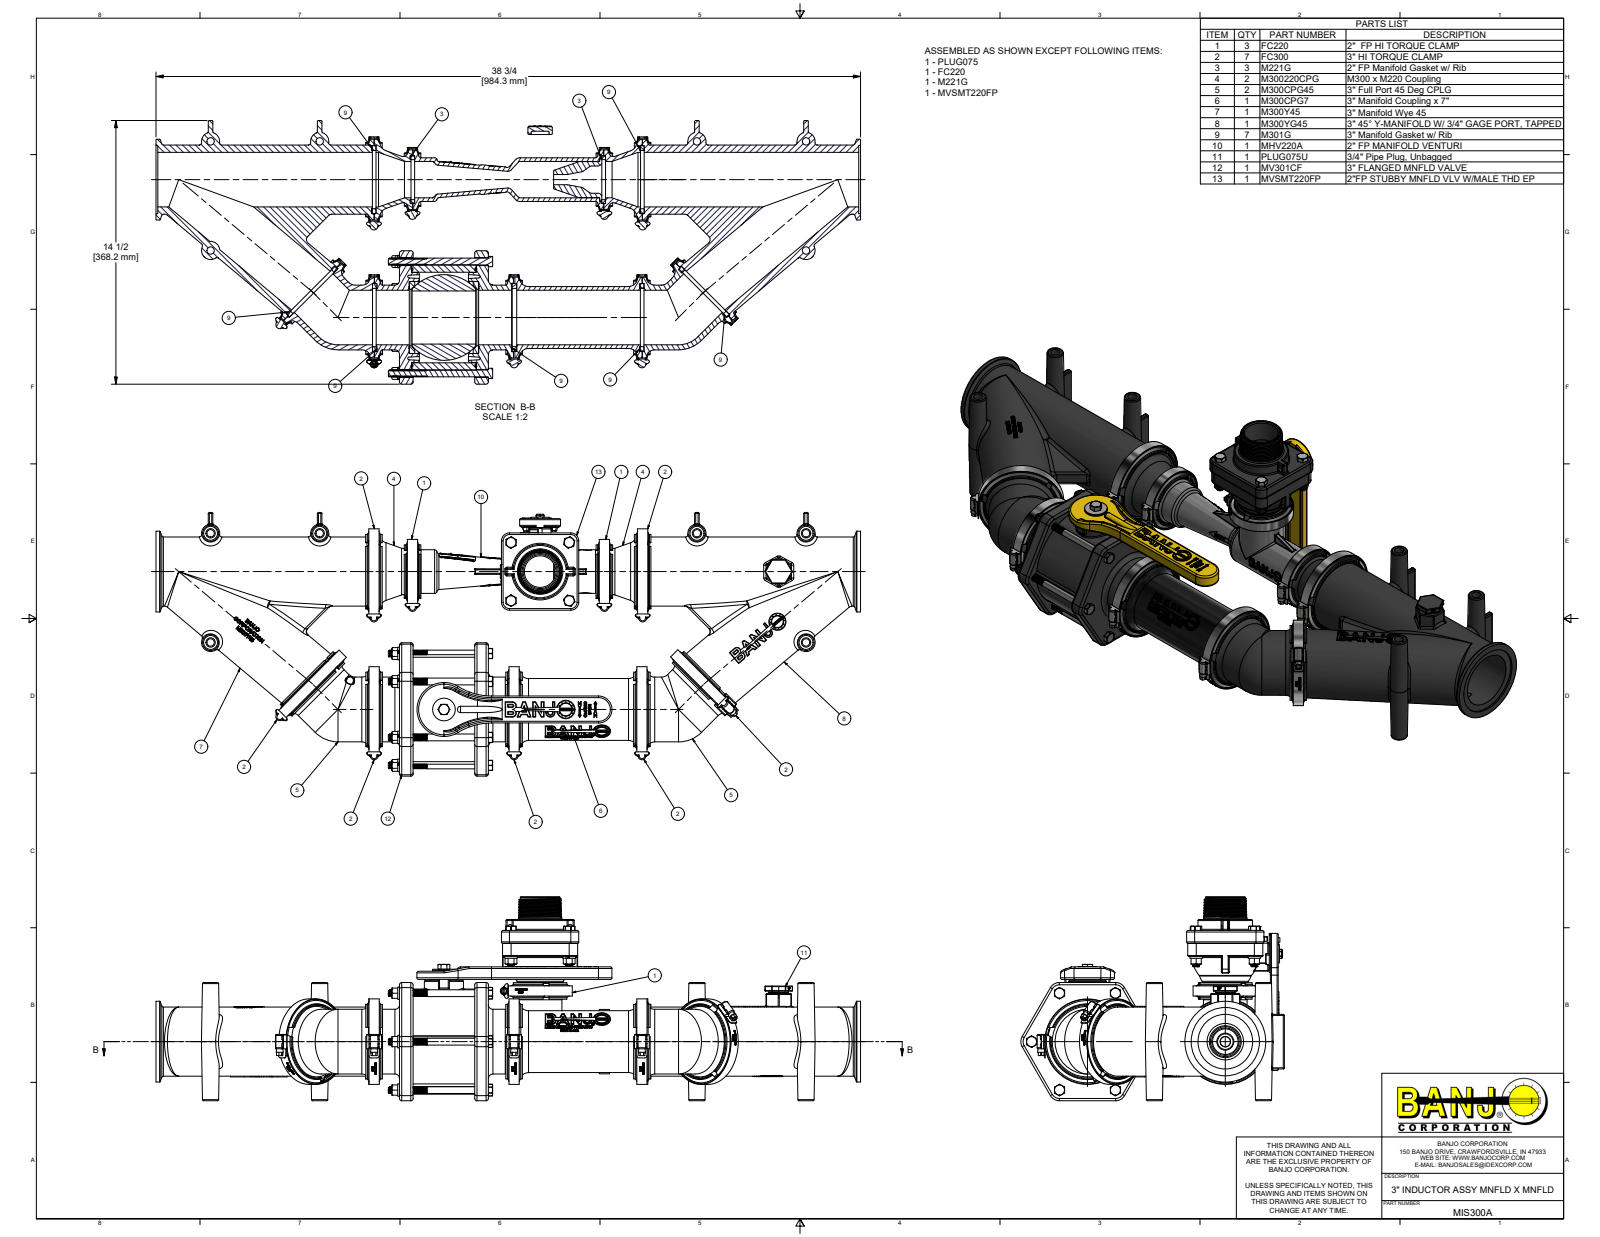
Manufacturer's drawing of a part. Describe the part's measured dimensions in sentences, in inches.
The part is named "MIS300A; M300YG45; M300Y45; M300CPG7 (+8 more)". Its 3-D file was written by "Autodesk Inventor 2019 (AUTOMOTIVE_DESIGN)". It is 100 solids with 12710 faces: 5194 planar, 2704 cylindrical and 4812 other. Overall it measures 46.025 by 38.75 by 14.494 inches. Its volume is 444.8 cubic inches and its surface area 3 521 square inches. Round holes: 12 of diameter 0.171, 11 of diameter 0.44, 10 of diameter 0.25, 10 of diameter 0.307, 10 of diameter 0.385, 9 of diameter 0.375, 6 of diameter 3, 5 of diameter 3.998, 4 of diameter 3.2, 4 of diameter 3.75, 4 of diameter 4.56, 4 of diameter 4.66. Round bosses or shafts: 60 of diameter 0.324, 10 of diameter 0.687, 6 of diameter 0.361, 6 of diameter 0.3, 5 of diameter 4.098, 4 of diameter 4.699, 4 of diameter 4.44, 4 of diameter 3.73. Partial cylindrical surfaces (rounded edges, fillets, slot ends): 138 of radius 0.06, 116 of radius 0.03, 72 of radius 0.125, 16 of radius 0.09, 12 of radius 0.219, 10 of radius 0.032, 10 of radius 0.32, 8 of radius 0.162. The main face-to-face distances are 0.1, 14.74, 0.665, 4.225, 4.89, 14.84, 0.09, 0.127, 0.538, 4.352. The hole center spacings are 2.805, 2.264, 5.418, 4.667, 5.433, 3.075, 0.813, 1.452.
